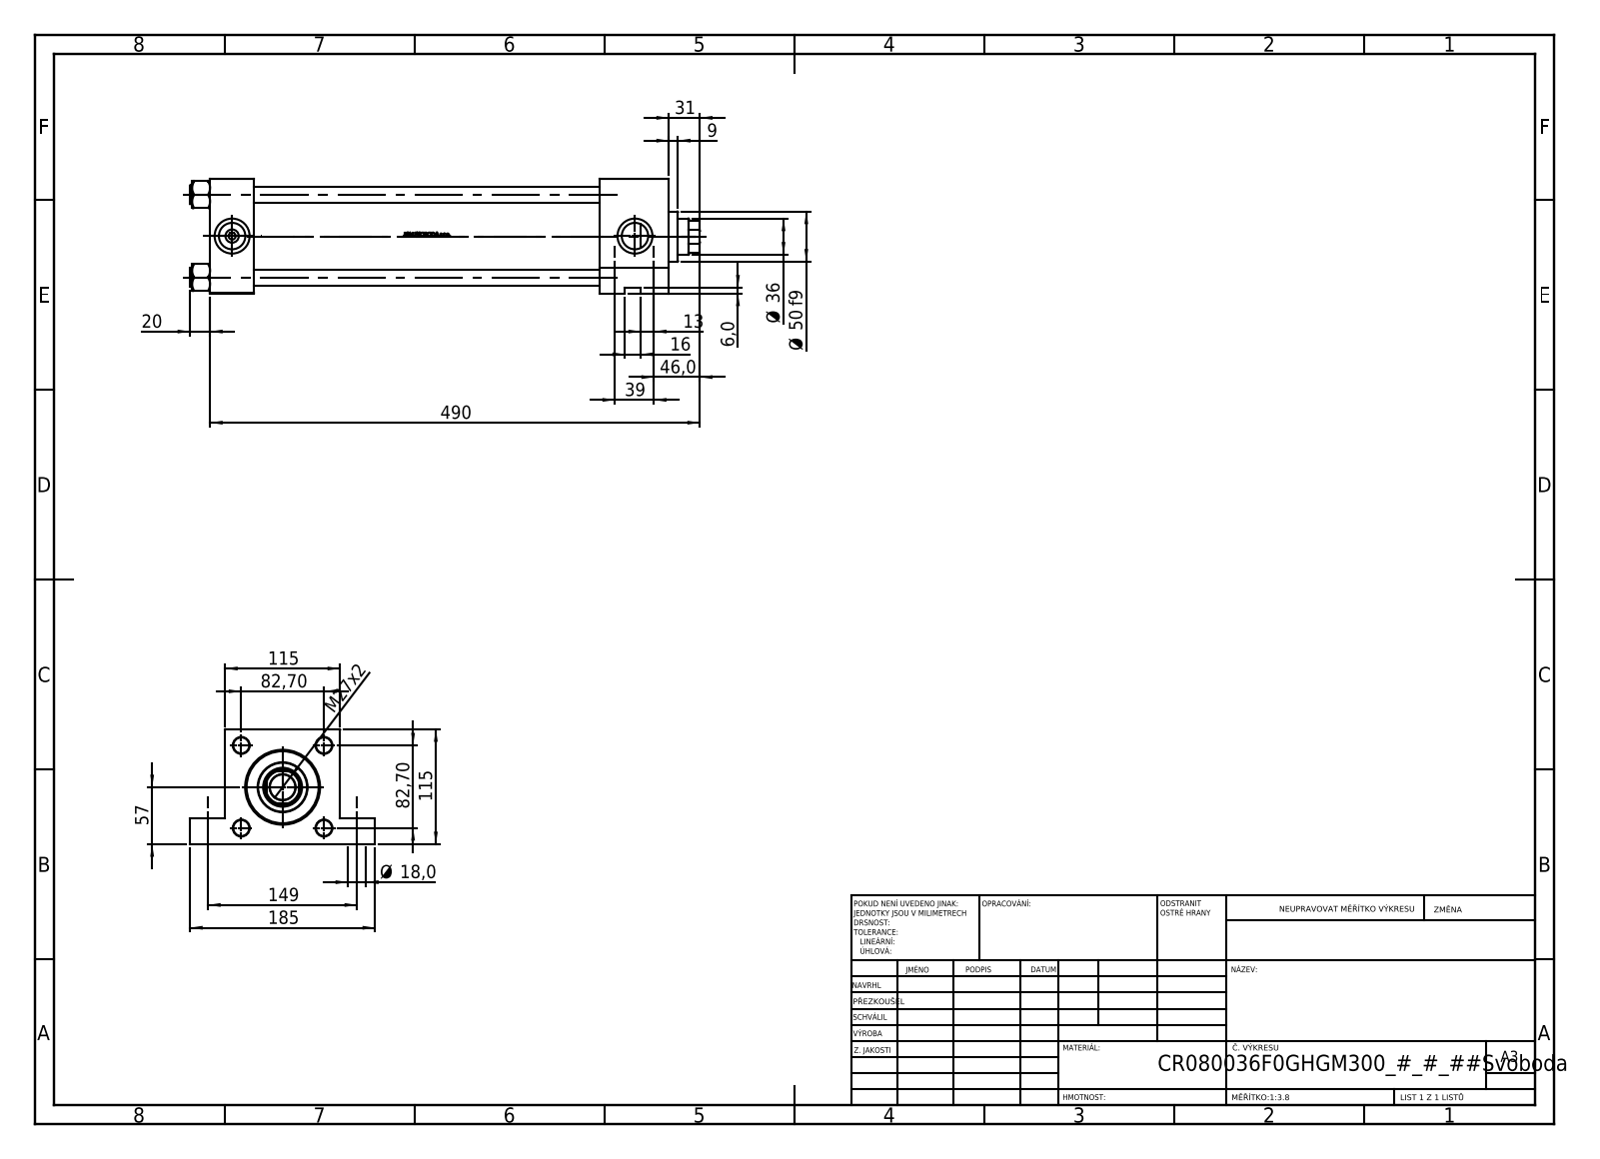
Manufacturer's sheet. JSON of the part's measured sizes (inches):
{"part_name": "V215CR_VCP_F; NUT_M5_F; V215CR_F_Body; V215_VC_A (+1 more)", "step_written_by": "SolidWorks 2019 (CONFIG_CONTROL_DESIGN)", "units": "inches", "bodies": {"solids": 11, "faces": 1151, "planar": 485, "cylindrical": 126, "other": 540}, "overall_size": [20.079, 7.283, 4.528], "volume_in3": 159.4, "surface_area_in2": 802.2, "round_holes": [[0.63, 4], [0.709, 4], [0.276, 2], [1.041, 2], [1.378, 2], [1.004, 1], [1.417, 1], [1.535, 1], [2.402, 1], [2.835, 1], [3.15, 1]], "round_bosses_or_shafts": [[0.748, 4], [3.386, 1], [1.969, 1]], "partial_cylinders_radius": [[0.689, 1]], "face_to_face_distances": [4.528, 1.732, 16.339, 18.071, 15.354, 13.622, 2.717, 16.941, 15.209, 1.587], "hole_center_spacings": [3.256, 1.535, 2.289, 2.316, 4.605, 5.866, 6.064, 15.866]}
